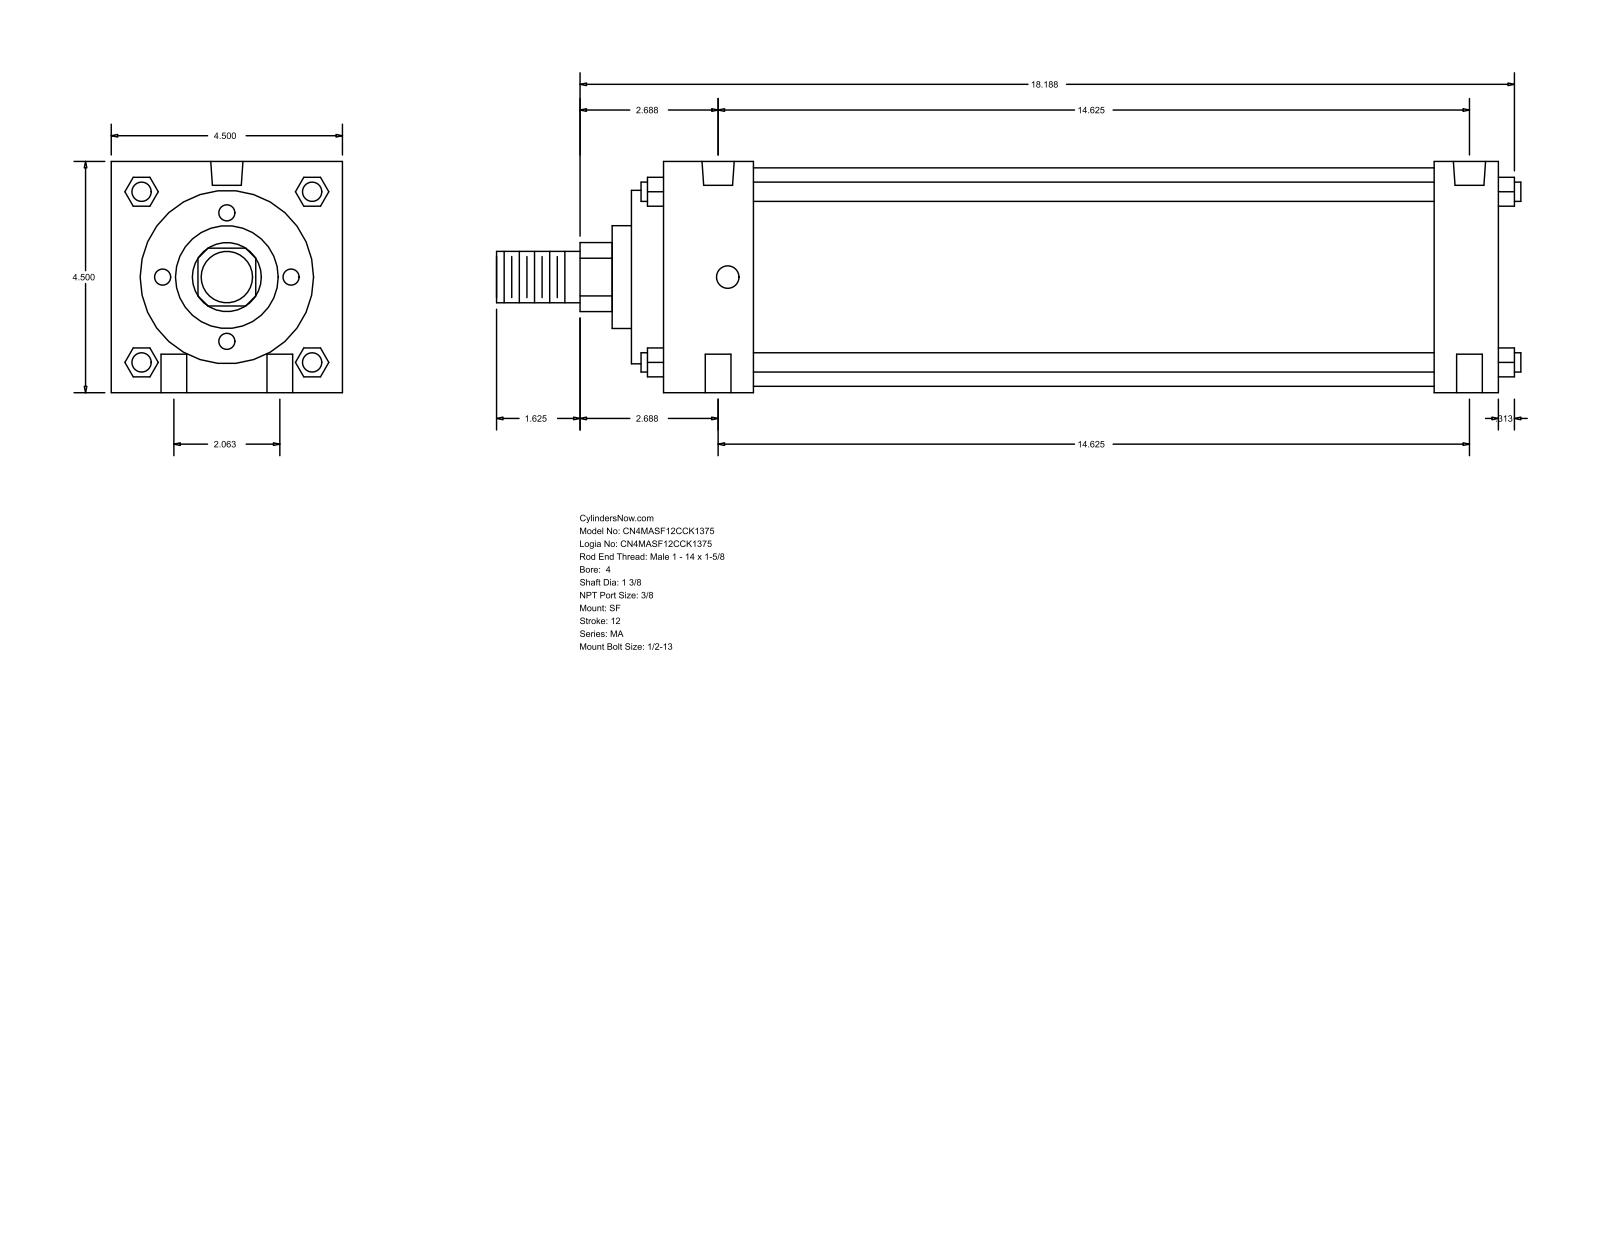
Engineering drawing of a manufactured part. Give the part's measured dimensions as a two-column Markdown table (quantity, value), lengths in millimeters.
| quantity | value |
| --- | --- |
| part name | MA_SF__0400_1.375 |
| STEP written by | GSSL Pune (CONFIG_CONTROL_DESIGN) |
| units | millimeters |
| bodies | 0 solids, 126 faces (95 planar, 31 cylindrical, 0 other) |
| overall size | 506.41 × 114.3 × 114.3 |
| round holes (diameter × count) | 12.7 × 4, 11.11 × 2, 15.93 × 2 |
| round bosses / shafts (diameter × count) | 9.53 × 4, 107.95 × 1, 85.72 × 1, 50.8 × 1, 34.92 × 1, 25.4 × 1 |
| partial cylindrical surfaces (radius × count) | 17.06 × 1 |
| main face-to-face distances | 114.3, 412.75, 428.62, 15.87, 396.87, 381, 31.75, 60.32, 44.45, 336.55 |
| hole center spacings | 26.19, 372.4, 371.48, 52.38, 375.15, 361.95 |
